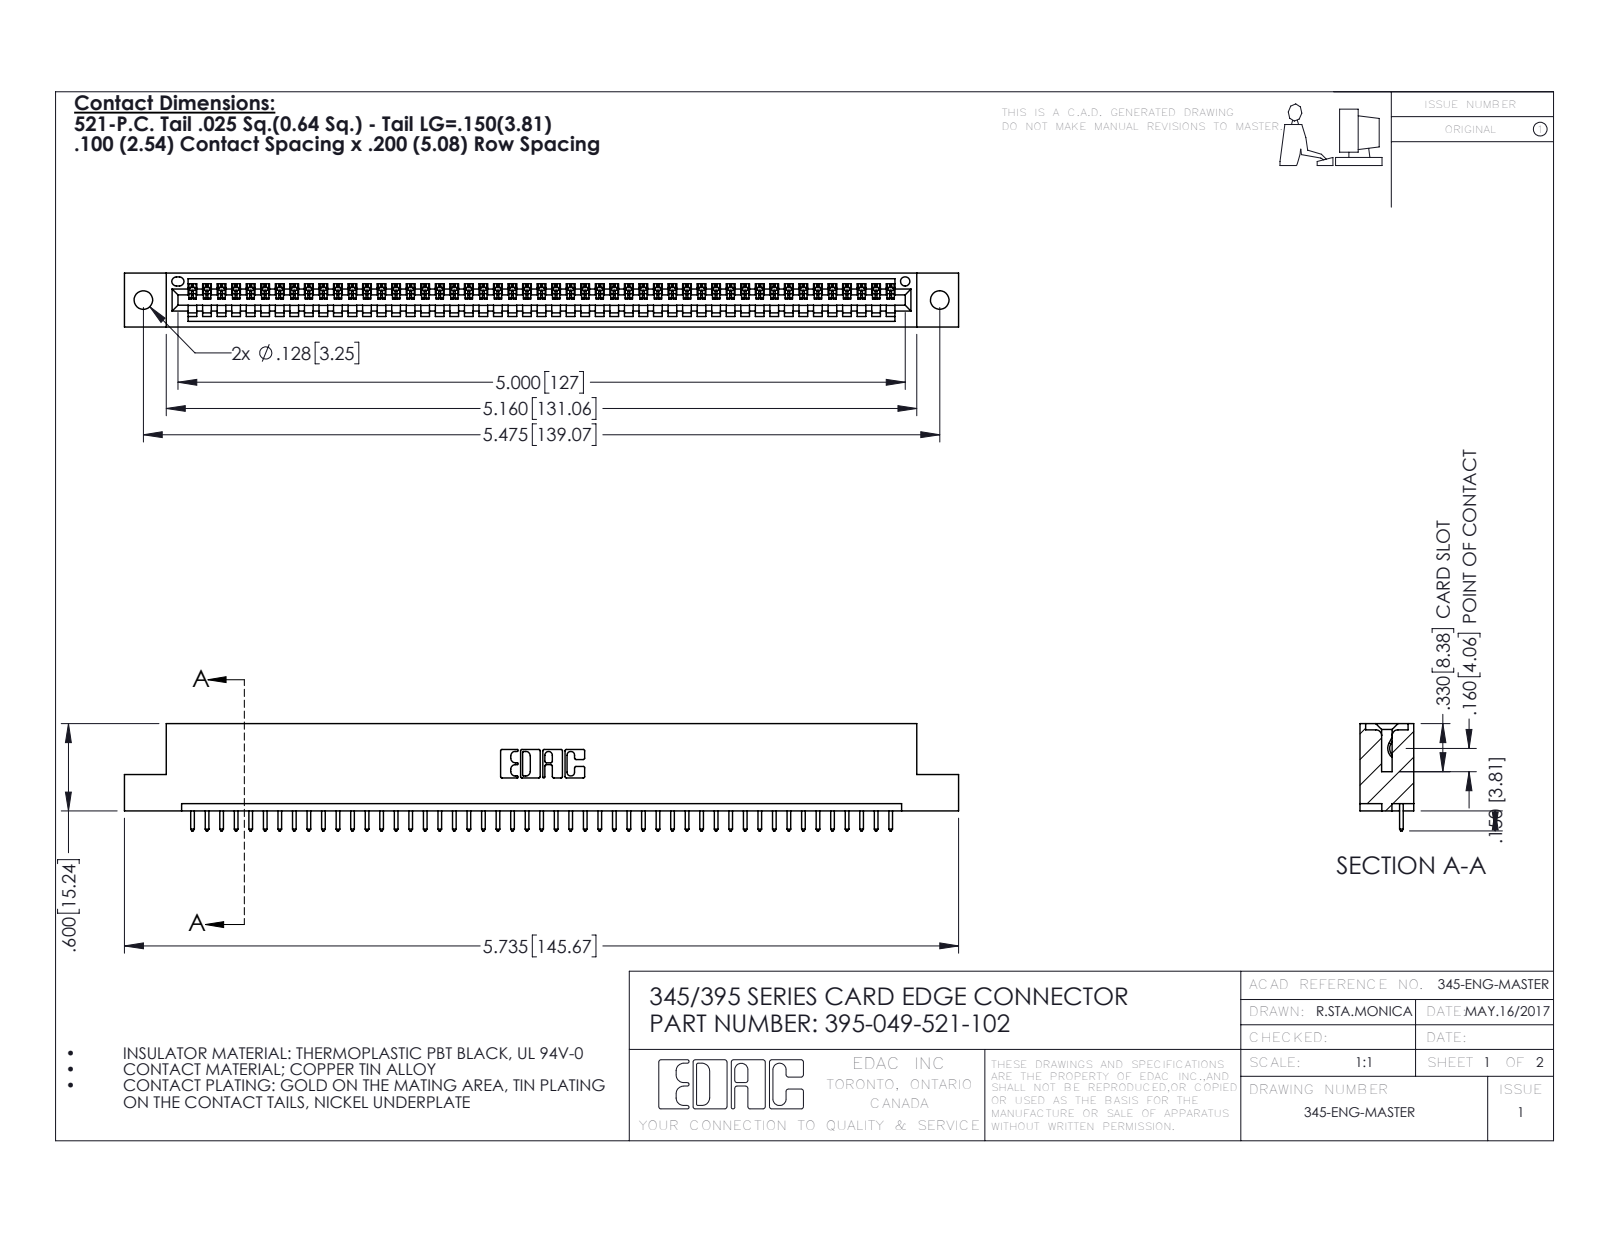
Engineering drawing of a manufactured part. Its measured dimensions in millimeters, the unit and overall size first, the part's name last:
Units: millimetres
Overall size (bounding box): 145.7 × 18.7 × 9.4
Round holes (diameter × count): ⌀3.3 ×2, ⌀1.6 ×1
Partial cylindrical surfaces — rounded edges, fillets, slot ends (radius × count): R0.2 ×98, R0.3 ×98, R0.3 ×22, R0.2 ×6, R0.8 ×6, R0.7 ×3, R0.8 ×2, R1 ×2
Main face-to-face distances: 7.6, 1.8, 9.4, 5.1, 2.5, 6.9, 0.6, 5.7, 3.8, 1.8
Hole centre spacings: 6.9, 133.1, 139.1
Volume: 13 700 mm³ · Surface area: 17 510 mm²
Bodies: 50 solids, 2968 faces (2040 planar, 928 cylindrical, 0 other)
Part name (STEP PRODUCT): 395-049-521-102; 345 Part_Flush Mounting Lugs - 0.128 Dia; 345-292-001_345-293-121
STEP written by: SolidWorks 2016 (CONFIG_CONTROL_DESIGN)
